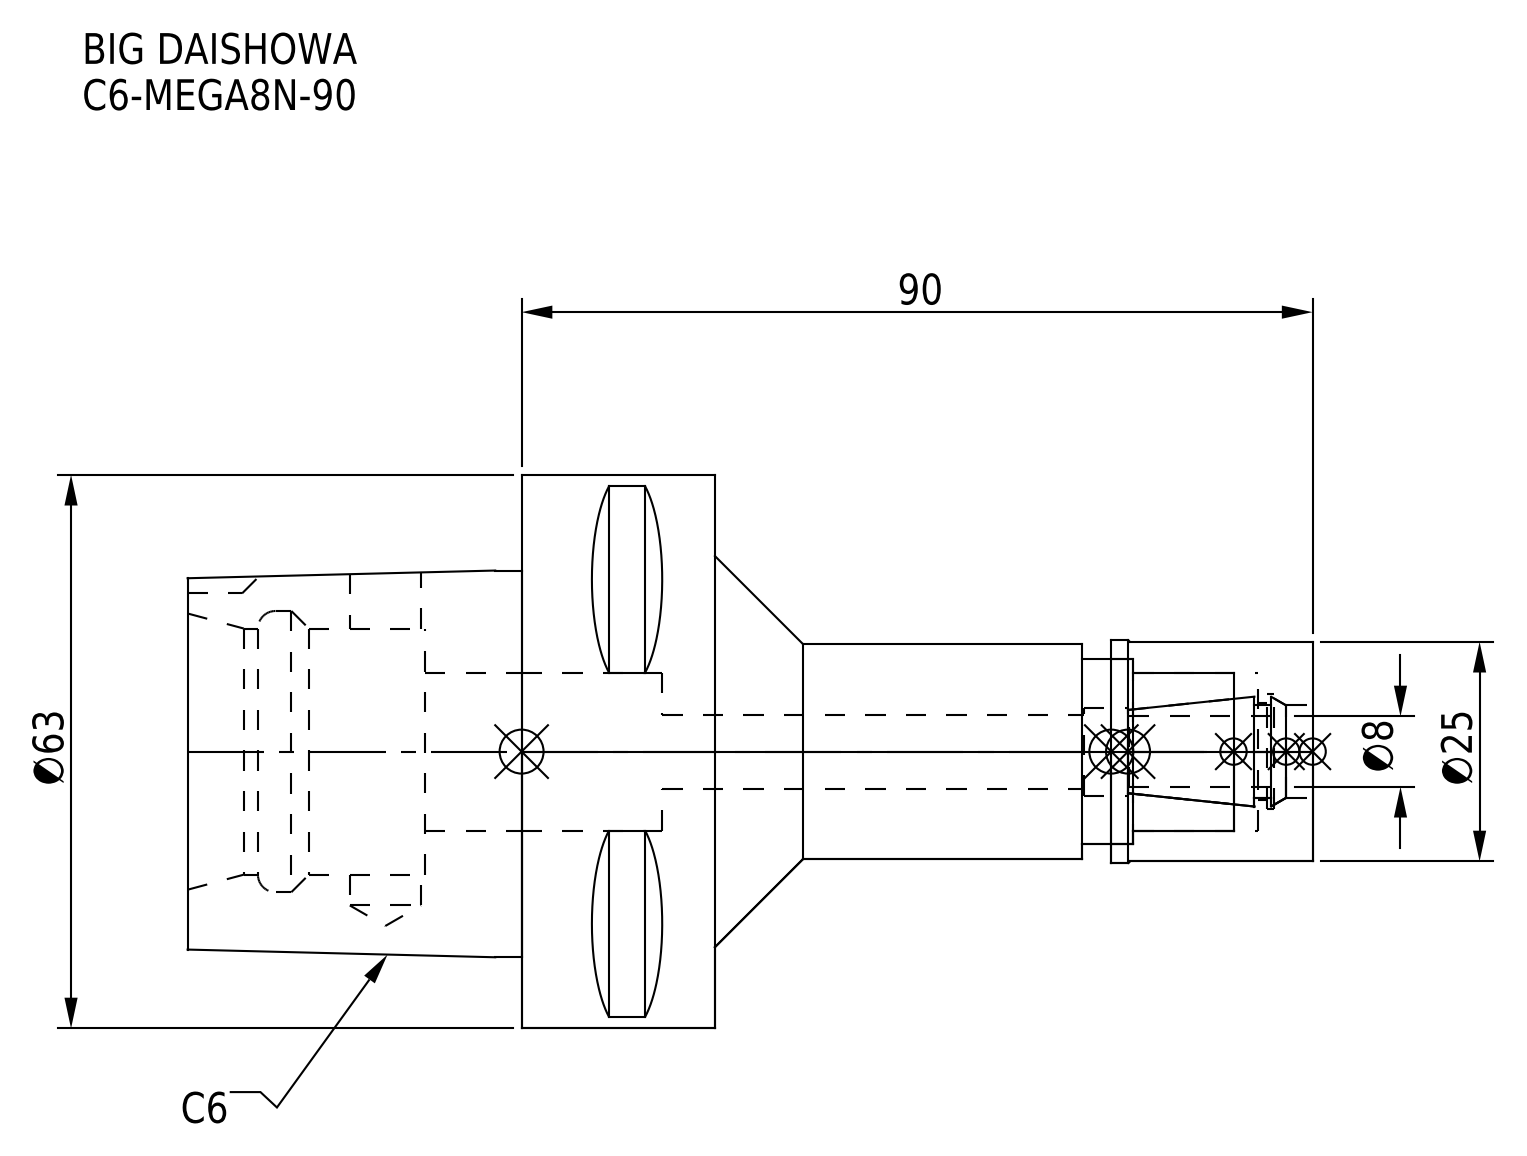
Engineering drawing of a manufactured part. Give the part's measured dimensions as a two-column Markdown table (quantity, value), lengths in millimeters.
| quantity | value |
| --- | --- |
| part name | C6-MEGA8N-90-080_ASM.stp; C6-MEGA8N-90-080-FreeParts; C6-MEGA8N-90; C6-MEGA8N-90_1.stp (+3 more) |
| STEP written by | SolidWorks 2019 (CONFIG_CONTROL_DESIGN) |
| units | millimeters |
| bodies | 2 solids, 95 faces (38 planar, 39 cylindrical, 18 other) |
| overall size | 128 × 63 × 63 |
| volume | 128 135 mm³ |
| surface area | 29 623 mm² |
| round holes (diameter × count) | 8.1 × 1, 8.4 × 1, 10 × 1, 10.5 × 1, 11 × 1, 13 × 1, 18 × 1, 21 × 1, 28 × 1, 32 × 1 |
| round bosses / shafts (diameter × count) | 63 × 1, 25.3 × 1, 25 × 1, 24.5 × 1 |
| partial cylindrical surfaces (radius × count) | 5 × 1 |
| main face-to-face distances | 22, 27, 60, 38, 68, 90, 128, 101, 33, 11 |
